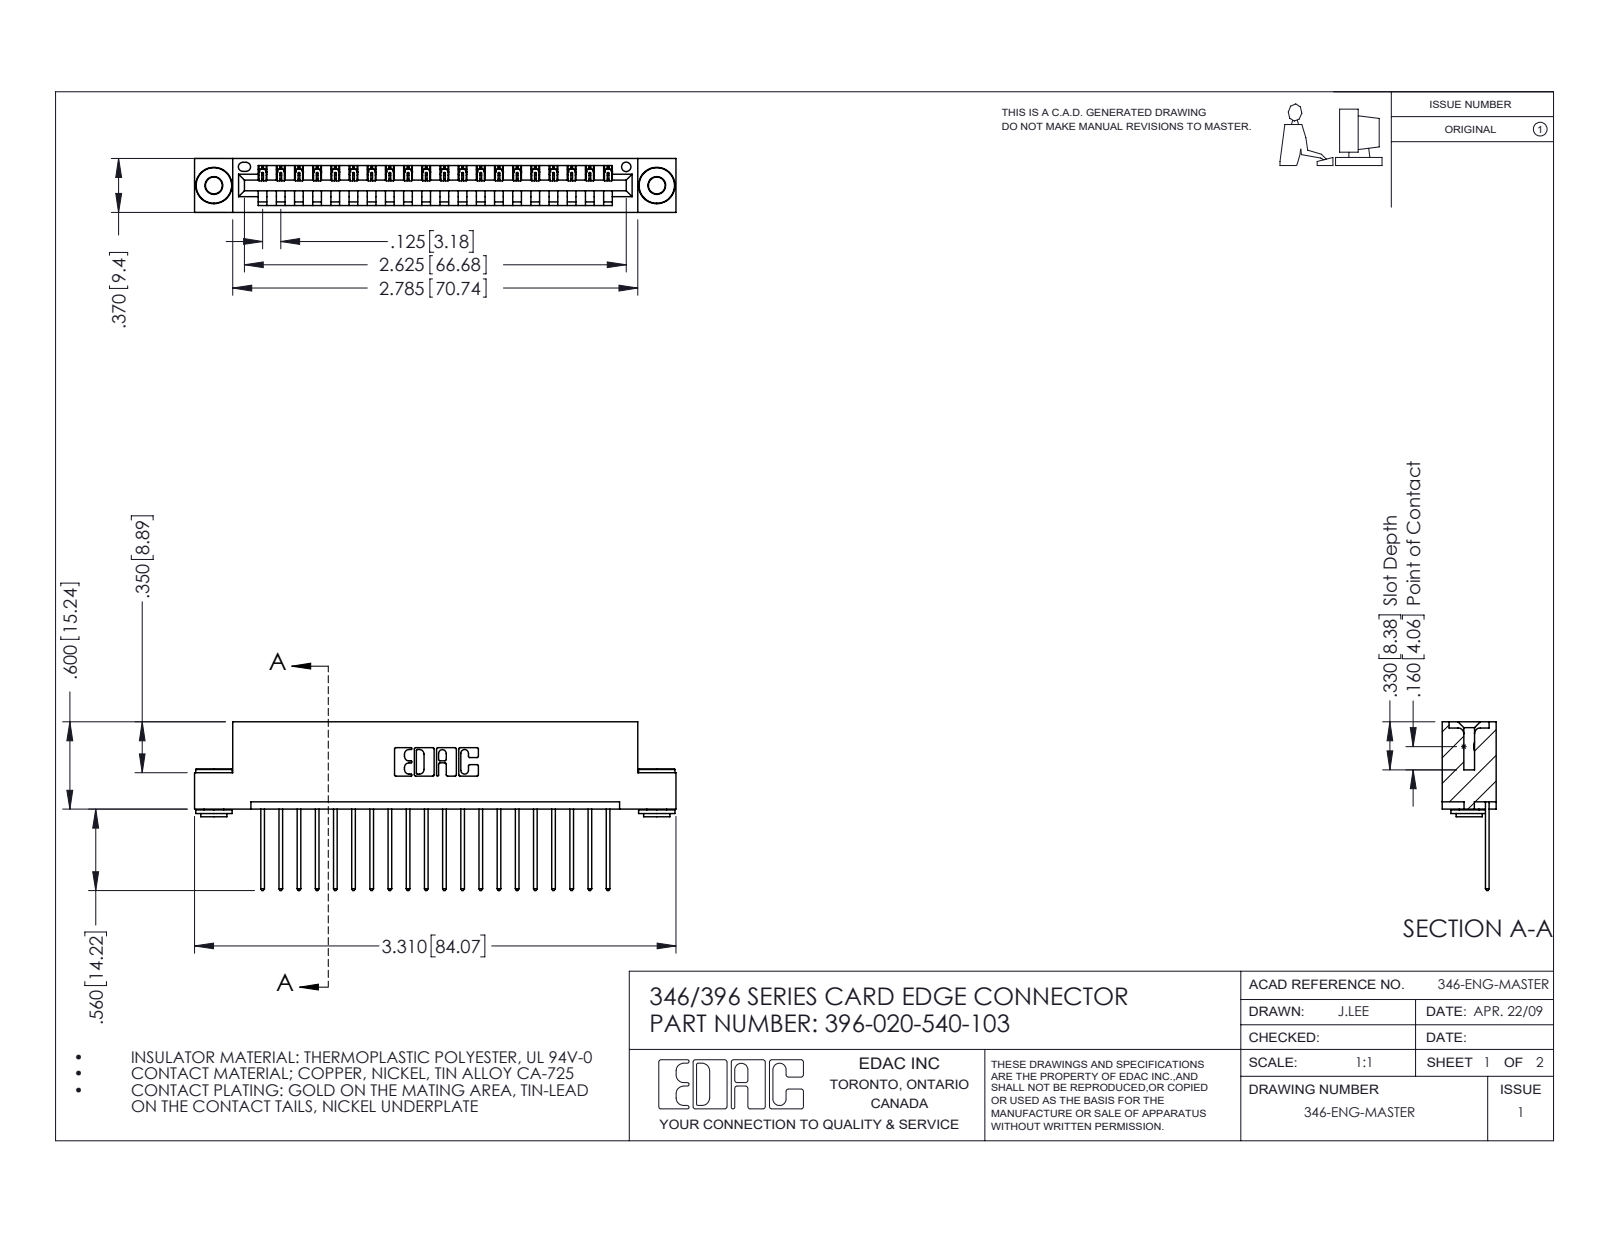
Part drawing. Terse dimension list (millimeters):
name: 346 Part_Flush Mounting Lugs - 0.156 Dia-TH; 396-020-540-103; 345-250-002_345-250-002-102; 345-292-001_345-293-140
written by: SolidWorks 2016 (CONFIG_CONTROL_DESIGN)
unit: mm
bodies: 23 solids, 1320 faces (886 planar, 426 cylindrical, 8 other)
size: 84.1 × 29.5 × 9.4
volume: 7 950 mm³; area: 10 110 mm²
holes: 2× ⌀2.9, 2× ⌀4, 1× ⌀1.6
bosses: 2× ⌀6.4, 2× ⌀4.6, 2× ⌀3.5
rounds: 40× R0.2, 40× R0.3, 22× R0.3, 6× R0.2, 6× R0.8, 3× R0.7, 2× R0.8, 2× R1
face distances: 1.2, 8.2, 6.4, 9.4, 0.6, 1.8, 7.6, 3.8, 5.6, 2.5
hole spacings: 6.2, 72.1, 77.3
